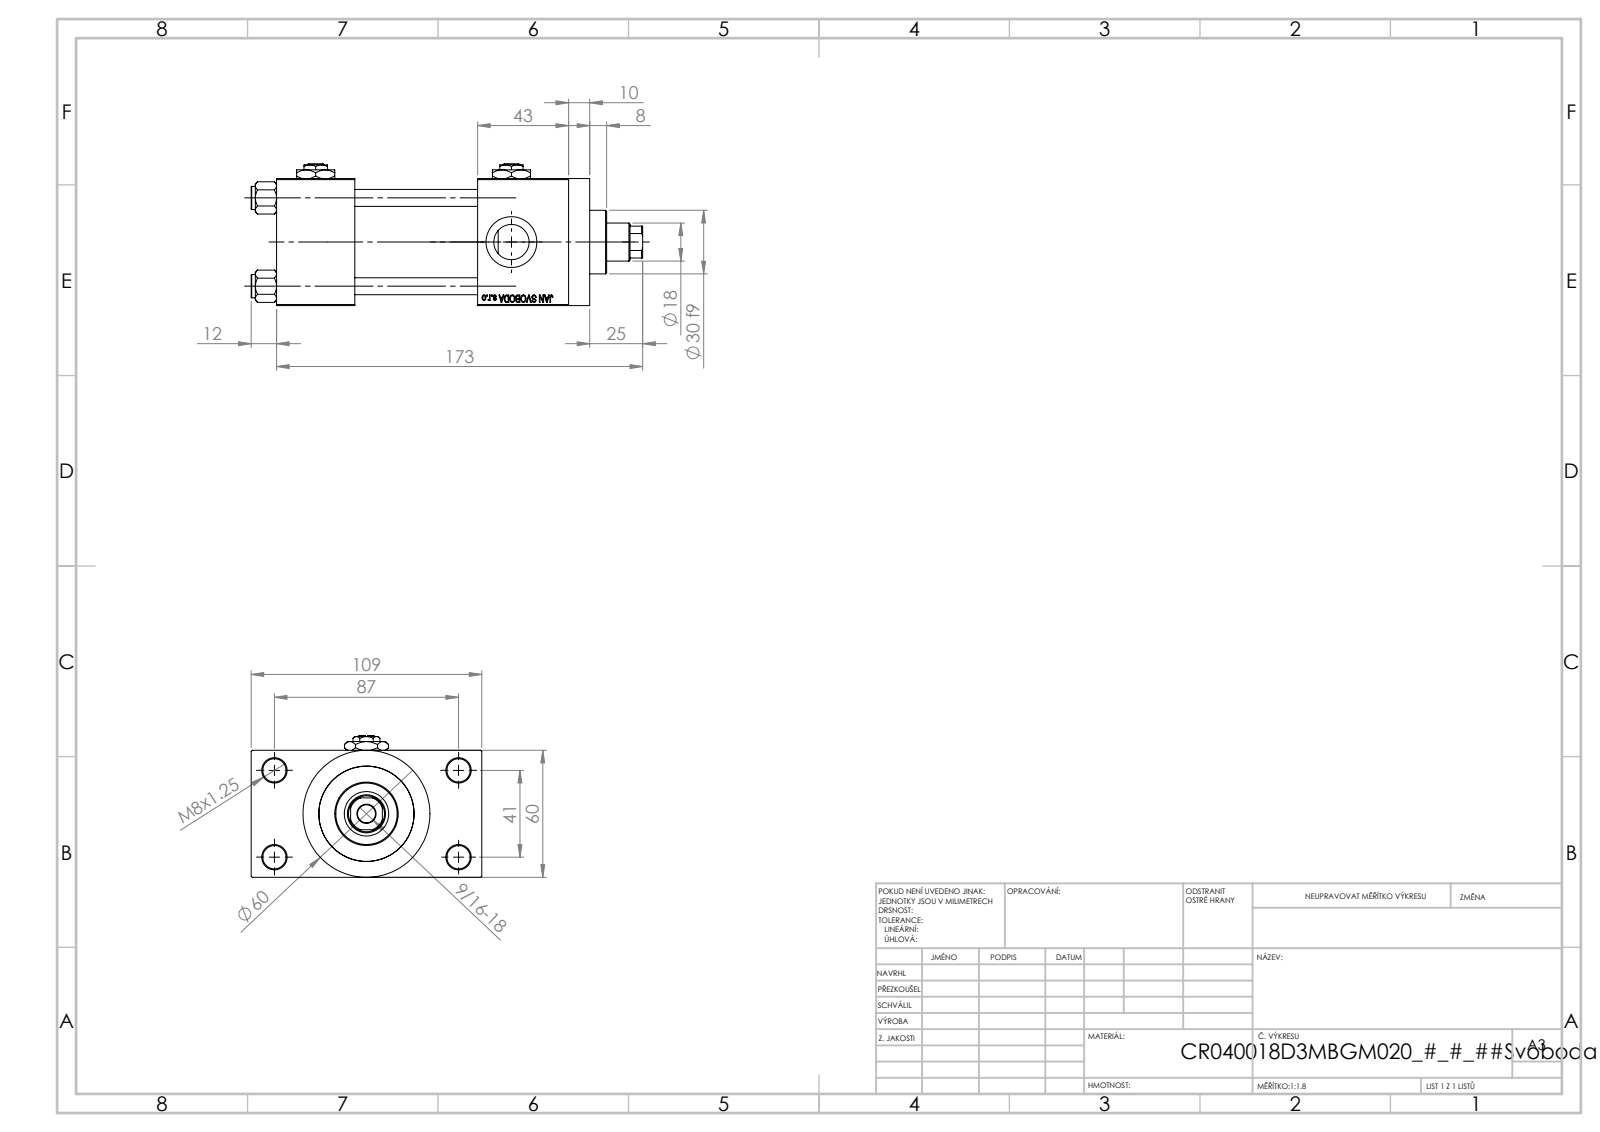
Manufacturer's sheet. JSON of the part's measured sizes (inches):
{"part_name": "V215CR_VCP_D; V215_VC_A; NUT_M5_D; Zatka_pro_OIL_PORT (+2 more)", "step_written_by": "SolidWorks 2019 (CONFIG_CONTROL_DESIGN)", "units": "inches", "bodies": {"solids": 13, "faces": 1205, "planar": 546, "cylindrical": 99, "other": 560}, "overall_size": [7.283, 4.291, 2.638], "volume_in3": 31.16, "surface_area_in2": 193.9, "round_holes": [[0.315, 4], [0.433, 4], [0.656, 4], [0.945, 4], [0.276, 3], [0.335, 1], [0.709, 1], [0.827, 1], [1.22, 1], [1.575, 1], [1.772, 1]], "round_bosses_or_shafts": [[0.433, 4], [2.362, 1], [1.811, 1], [1.181, 1]], "partial_cylinders_radius": [[0.335, 1]], "face_to_face_distances": [2.362, 2.283, 3.327, 0.965, 1.457, 3.74, 1.693, 5.433, 3.976, 0.394], "hole_center_spacings": [0.892, 1.161, 1.642, 1.856, 1.893, 2.533, 3.011, 1.614]}
